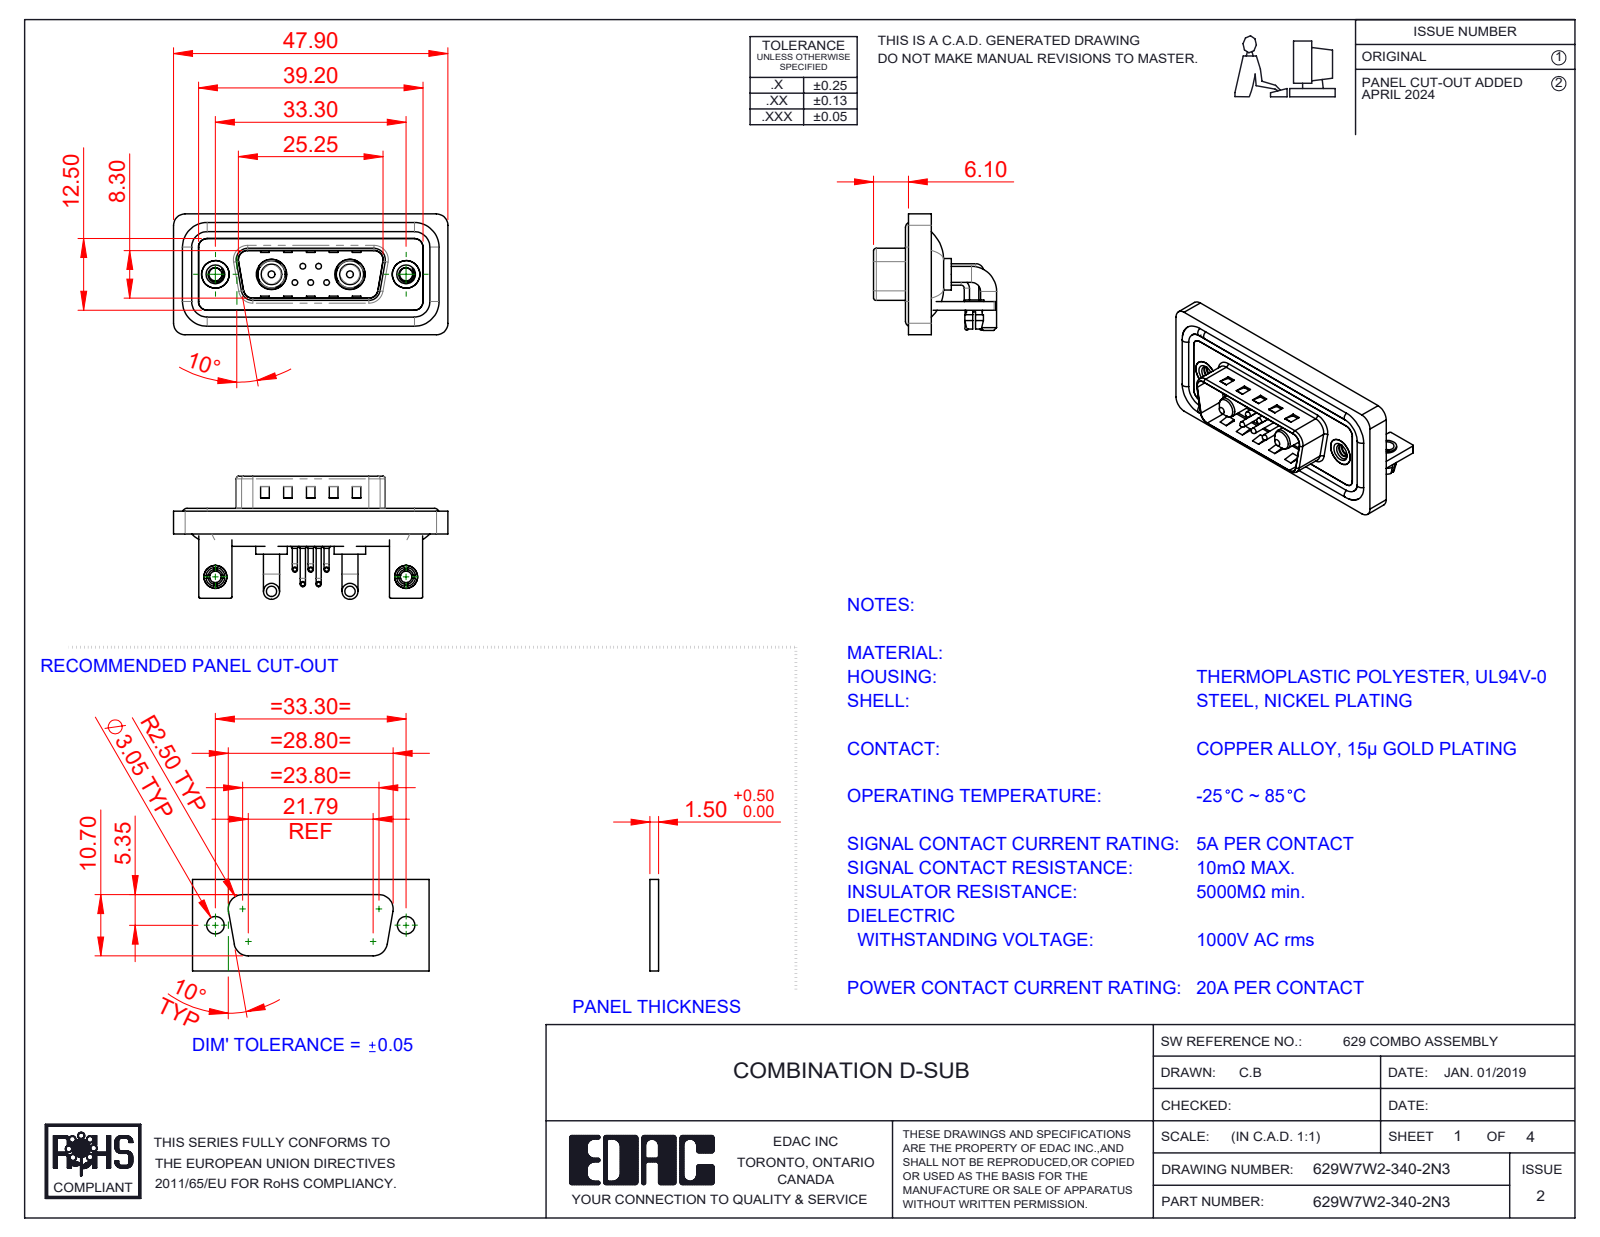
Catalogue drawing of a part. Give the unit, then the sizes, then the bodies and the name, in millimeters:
Units: millimetres
Overall size (bounding box): 47.9 × 21.5 × 21.1
Round holes (diameter × count): ⌀2 ×7, ⌀0.75 ×5, ⌀1.6 ×5, ⌀2.26 ×2, ⌀2.5 ×2, ⌀3.2 ×2, ⌀4 ×2, ⌀4.8 ×2, ⌀4.85 ×2, ⌀5 ×2, ⌀5.3 ×2
Round bosses / shafts (diameter × count): ⌀0.9 ×10, ⌀1.5 ×5, ⌀1 ×5, ⌀0.65 ×5, ⌀2.8 ×4, ⌀1.6 ×4, ⌀5.5 ×2, ⌀5.2 ×2
Partial cylindrical surfaces — rounded edges, fillets, slot ends (radius × count): R2 ×21, R1.5 ×18, R0.25 ×16, R0.5 ×9, R1.6 ×8, R1.01 ×5, R0.6 ×4, R0.65 ×4
Main face-to-face distances: 0.4, 1.5, 0.8, 2.9, 2.1, 1.1, 1.6, 1.2, 3.7, 4.5
Hole centre spacings: 3.16, 2.77, 9.8, 23.5, 33.3, 4.31, 4.33, 5.03
Volume: 5 994 mm³ · Surface area: 9 938 mm²
Bodies: 20 solids, 1215 faces (585 planar, 456 cylindrical, 174 other)
Part name (STEP PRODUCT): 629Combo Stabilizer Bracket; 629Combo Housing_7W2; 629Combo Board Lock; Power Pin_20A RA (+7 more)
STEP written by: SolidWorks 2023 (CONFIG_CONTROL_DESIGN)
